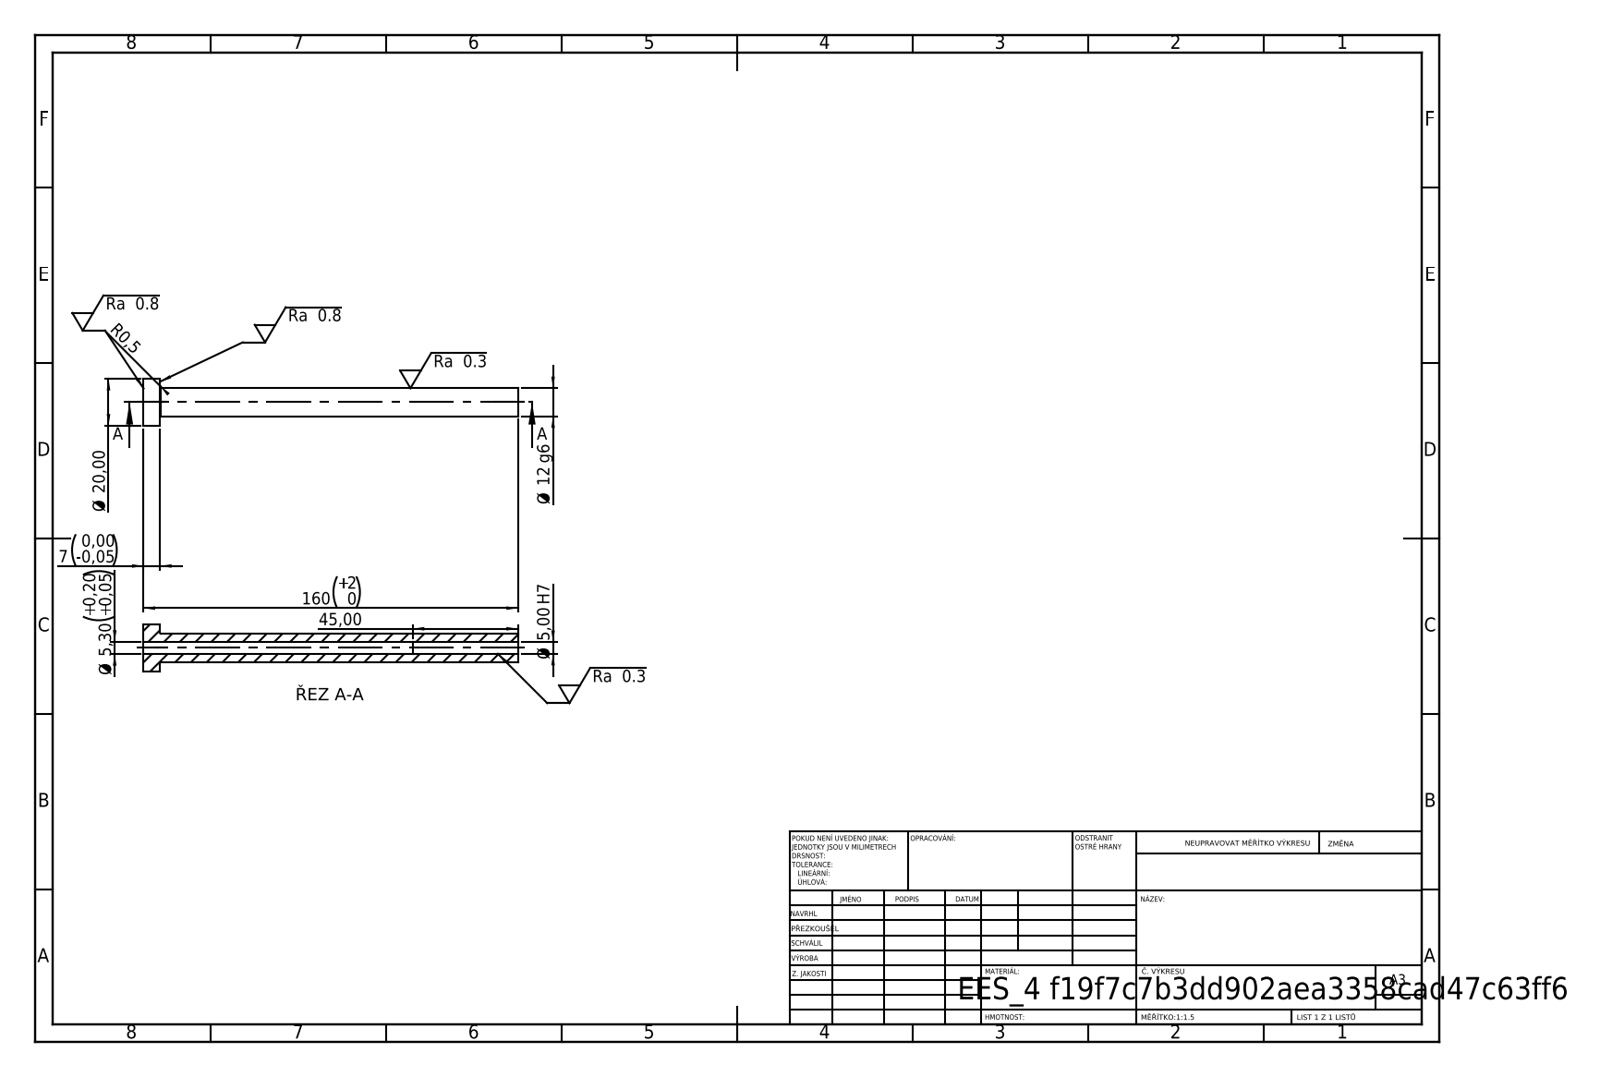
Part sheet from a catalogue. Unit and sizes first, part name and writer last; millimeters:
Units: millimetres
Overall size (bounding box): 160 × 20 × 20
Round holes (diameter × count): ⌀5 ×1, ⌀5.3 ×1
Round bosses / shafts (diameter × count): ⌀20 ×1, ⌀12 ×1
Main face-to-face distances: 7, 160, 153, 115, 108, 45
Volume: 16 084 mm³ · Surface area: 9 411 mm²
Bodies: 1 solid, 14 faces (4 planar, 8 cylindrical, 2 other)
STEP written by: SolidWorks 2019 (CONFIG_CONTROL_DESIGN)
